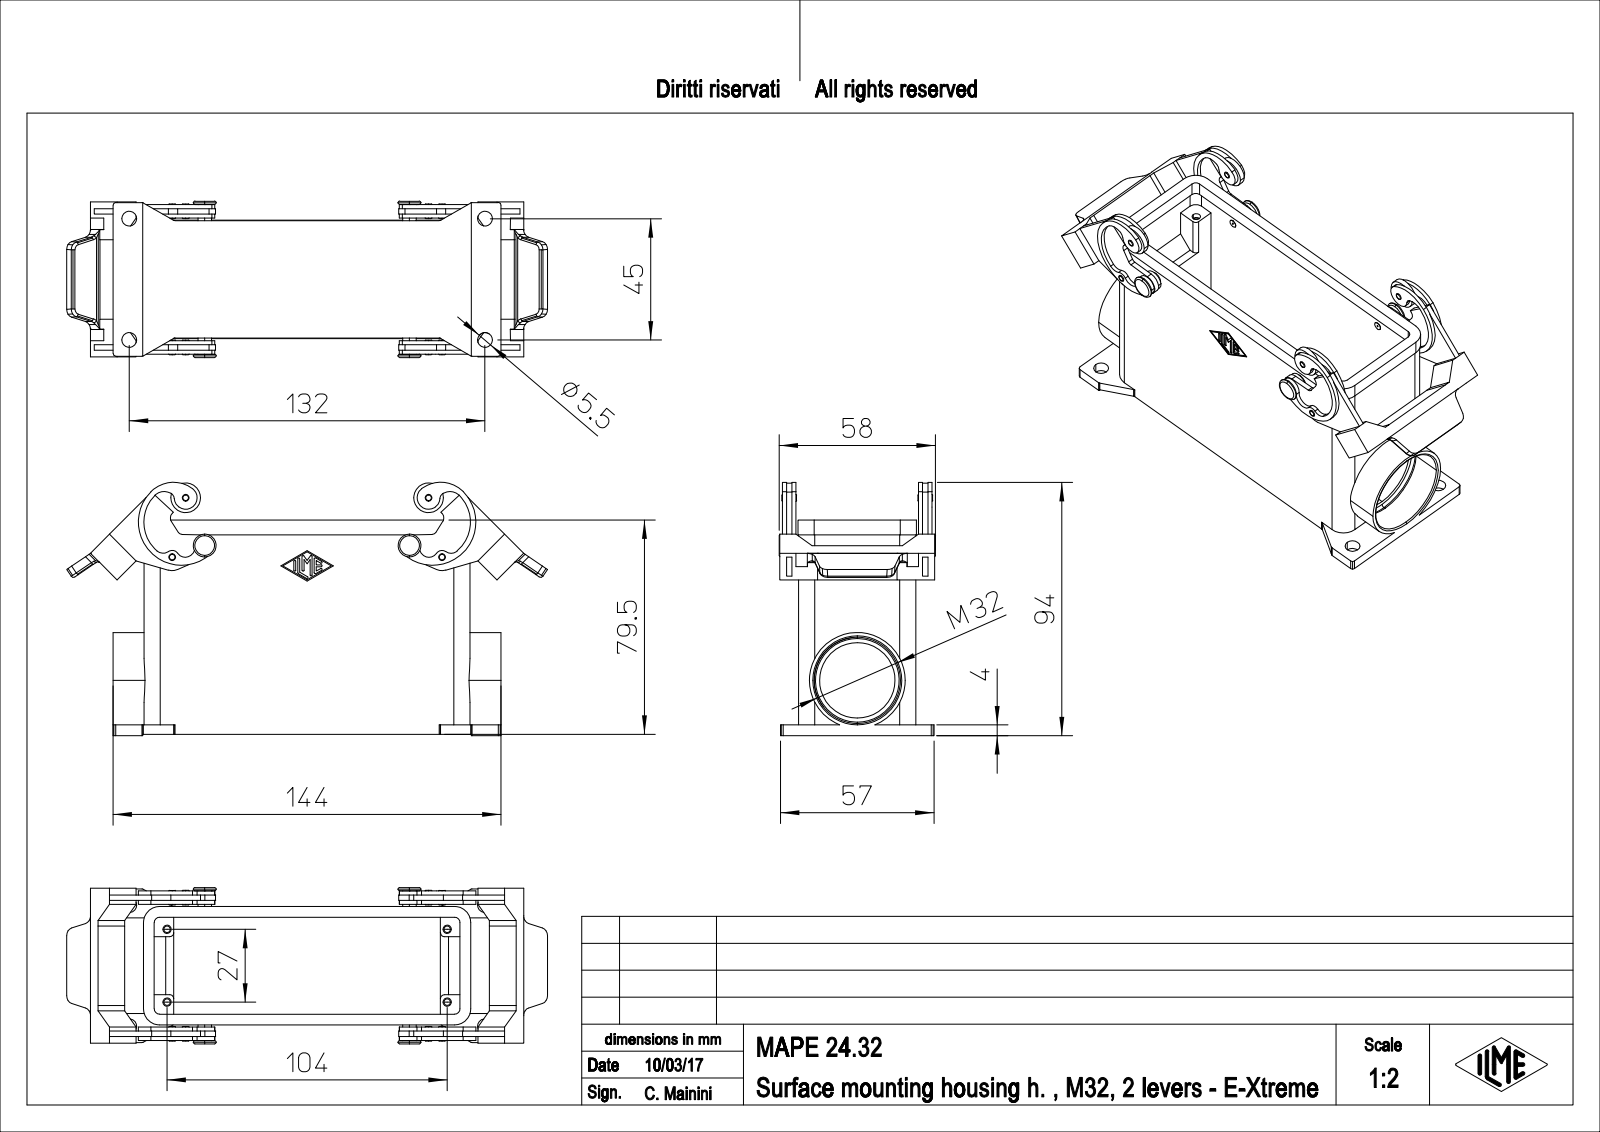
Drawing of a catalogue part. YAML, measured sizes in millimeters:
part_name: "MAPE_24.32"
step_written_by: "PTC Creo Elements/Direct Modeling 19.0E 27-Jun-2016 (C) Parametric Technology GmbH (AUTOMOTIVE_DESIGN)"
units: millimeters
bodies: {solids: 1, faces: 757, planar: 329, cylindrical: 328, other: 100}
overall_size: [178.49, 93.94, 58]
volume: 141860
surface_area: 82440
round_holes:
  - {diameter: 2, count: 4}
  - {diameter: 2.46, count: 4}
  - {diameter: 3.1, count: 4}
  - {diameter: 5.5, count: 4}
  - {diameter: 2.5, count: 2}
  - {diameter: 28, count: 1}
  - {diameter: 32, count: 1}
round_bosses_or_shafts:
  - {diameter: 11, count: 2}
  - {diameter: 5, count: 2}
  - {diameter: 3, count: 2}
  - {diameter: 35.5, count: 1}
partial_cylinders:
  - {radius: 1, count: 20}
  - {radius: 0.38, count: 14}
  - {radius: 3, count: 12}
  - {radius: 6, count: 8}
  - {radius: 1.5, count: 6}
  - {radius: 2.5, count: 6}
  - {radius: 2, count: 4}
  - {radius: 3.5, count: 4}
face_to_face_distances: [3, 40.5, 43.5, 3.5, 37.5, 4, 50.5, 4.5, 11, 110]
hole_center_spacings: [16.64, 38.63, 118.34, 123.37, 22.56, 27, 45, 97.67]
